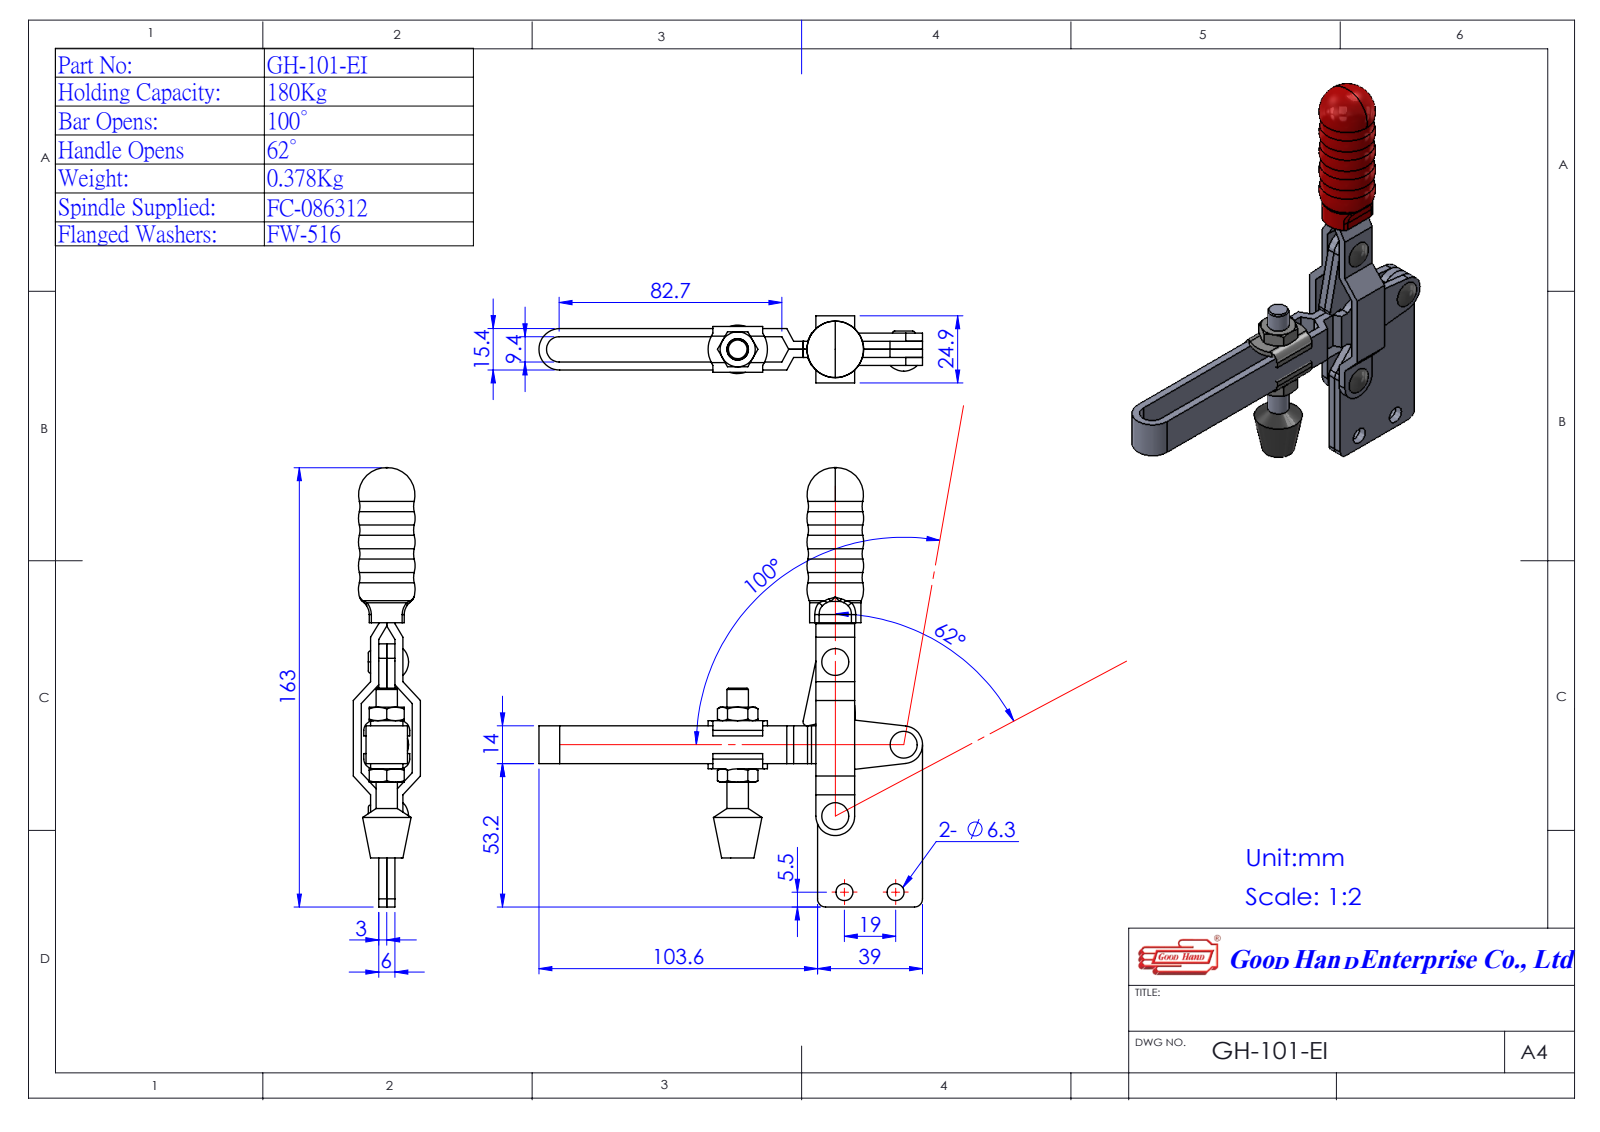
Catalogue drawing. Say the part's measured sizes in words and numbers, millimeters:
The part is named "Group6^GH-101-EI(簡化)-1; Group5^GH-101-EI(簡化)-1; Group2^GH-101-EI(簡化)-1; GH-101-EI(簡化)-1 (+2 more)". Its 3-D file was written by "SolidWorks 2016 (AUTOMOTIVE_DESIGN)". It is 5 solids with 324 faces: 136 planar, 94 cylindrical and 94 other. Overall it measures 163.01 by 142.4 by 24.9 millimeters. Its volume is 62 143 cubic millimeters and its surface area 32 774 square millimeters. Round holes: 4 of diameter 5, 2 of diameter 6.3. Round bosses or shafts: 2 of diameter 6.3, 1 of diameter 7.93. Partial cylindrical surfaces (rounded edges, fillets, slot ends): 4 of radius 0.5, 4 of radius 1.2, 4 of radius 2, 4 of radius 3, 4 of radius 3.6, 2 of radius 6, 2 of radius 6.75, 2 of radius 11.04. The main face-to-face distances are 3, 6, 10.7, 1.7, 4.7, 7.7, 12.4, 13.7, 1.3, 9. The hole center spacings are 19, 24.2, 26.53, 28.4, 30.72, 36.01, 36.71, 39.85.
